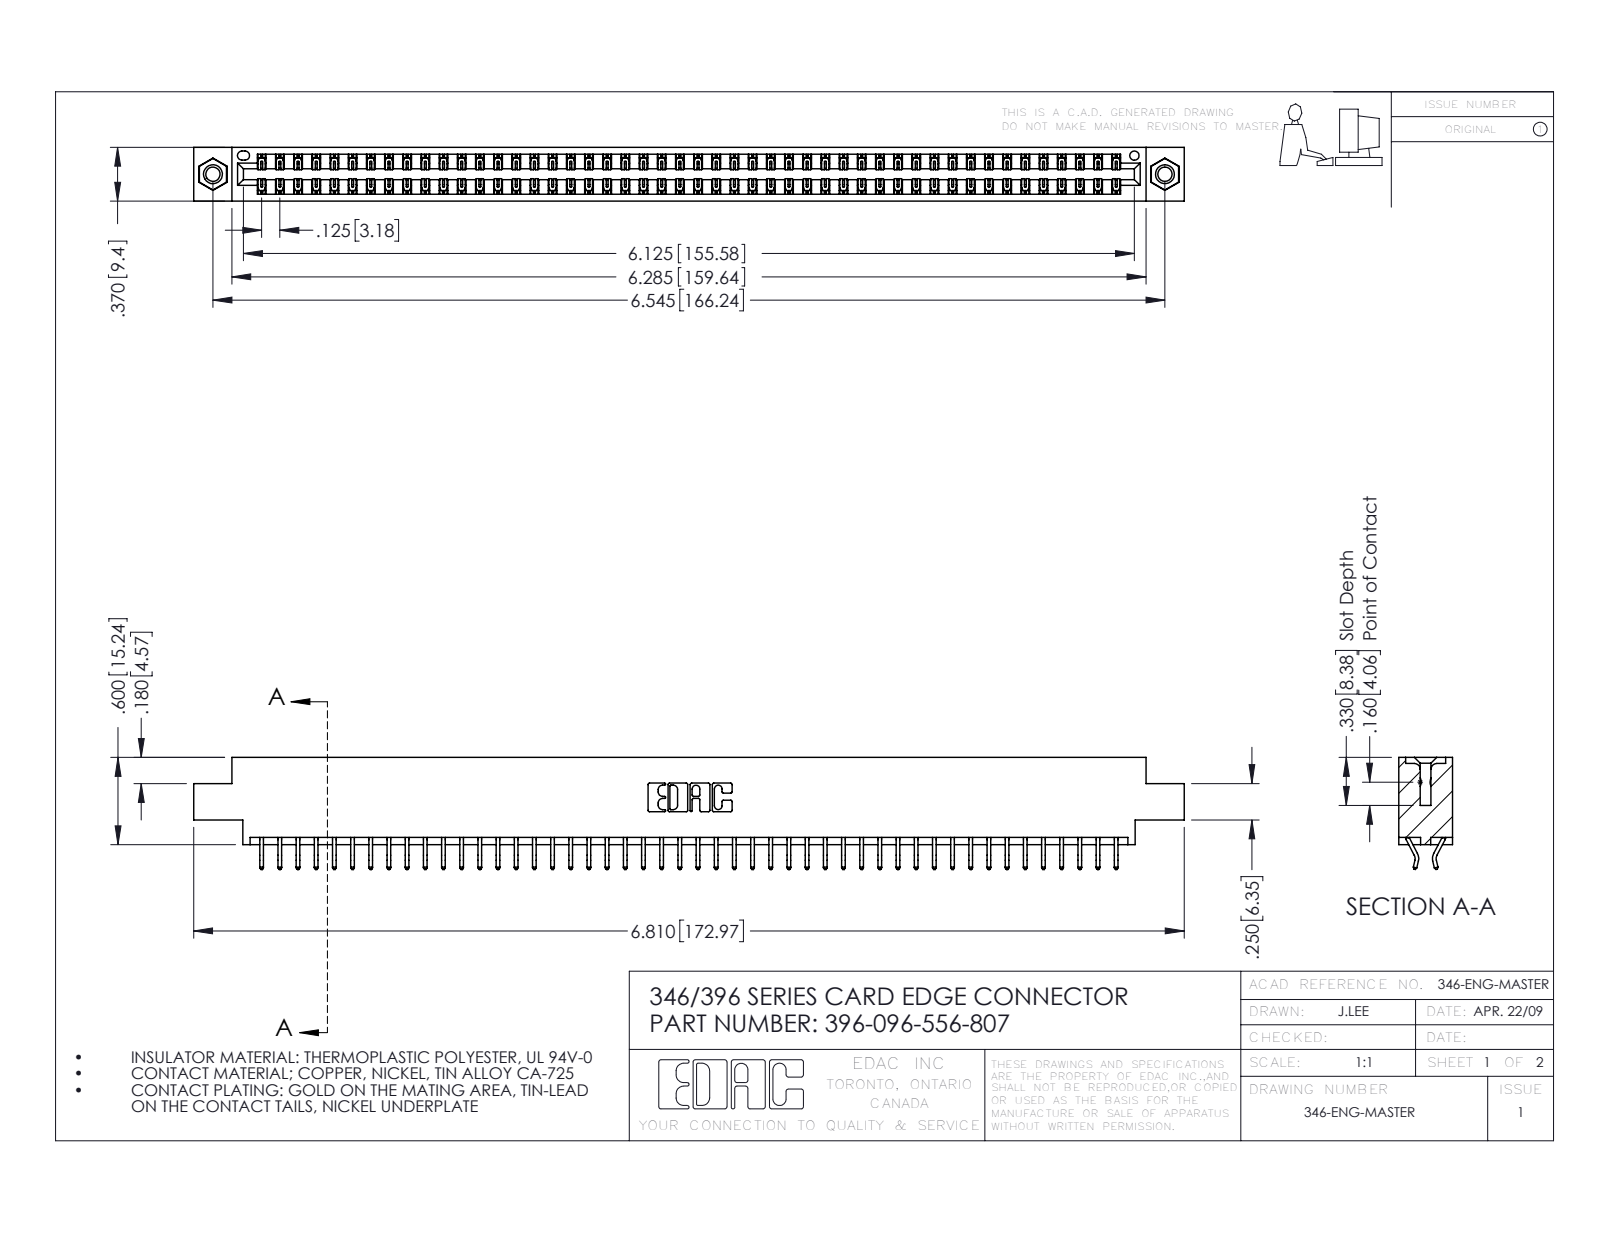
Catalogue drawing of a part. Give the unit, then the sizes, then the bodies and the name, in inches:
Units: inches
Overall size (bounding box): 6.81 × 0.77 × 0.37
Round holes (diameter × count): ⌀0.098 ×2, ⌀0.125 ×2, ⌀0.156 ×2, ⌀0.064 ×1
Round bosses / shafts (diameter × count): ⌀0.155 ×2
Partial cylindrical surfaces — rounded edges, fillets, slot ends (radius × count): R0.006 ×144, R0.01 ×22, R0.007 ×6, R0.031 ×6, R0.026 ×3, R0.01 ×2, R0.014 ×2, R0.022 ×2
Main face-to-face distances: 0.048, 0.322, 0.37, 0.25, 0.025, 0.072, 0.298, 0.275, 0.222, 0.148
Hole centre spacings: 0.246, 6.336, 6.545
Volume: 1.022 in³ · Surface area: 36.01 in²
Bodies: 99 solids, 5754 faces (3856 planar, 1882 cylindrical, 16 other)
Part name (STEP PRODUCT): 396-096-556-807; 345-292-001_556 Tail; 346 Part_0.170 Offset - 0.156 Dia-TI; 345-250-001_345-250-005-103
STEP written by: SolidWorks 2016 (CONFIG_CONTROL_DESIGN)
